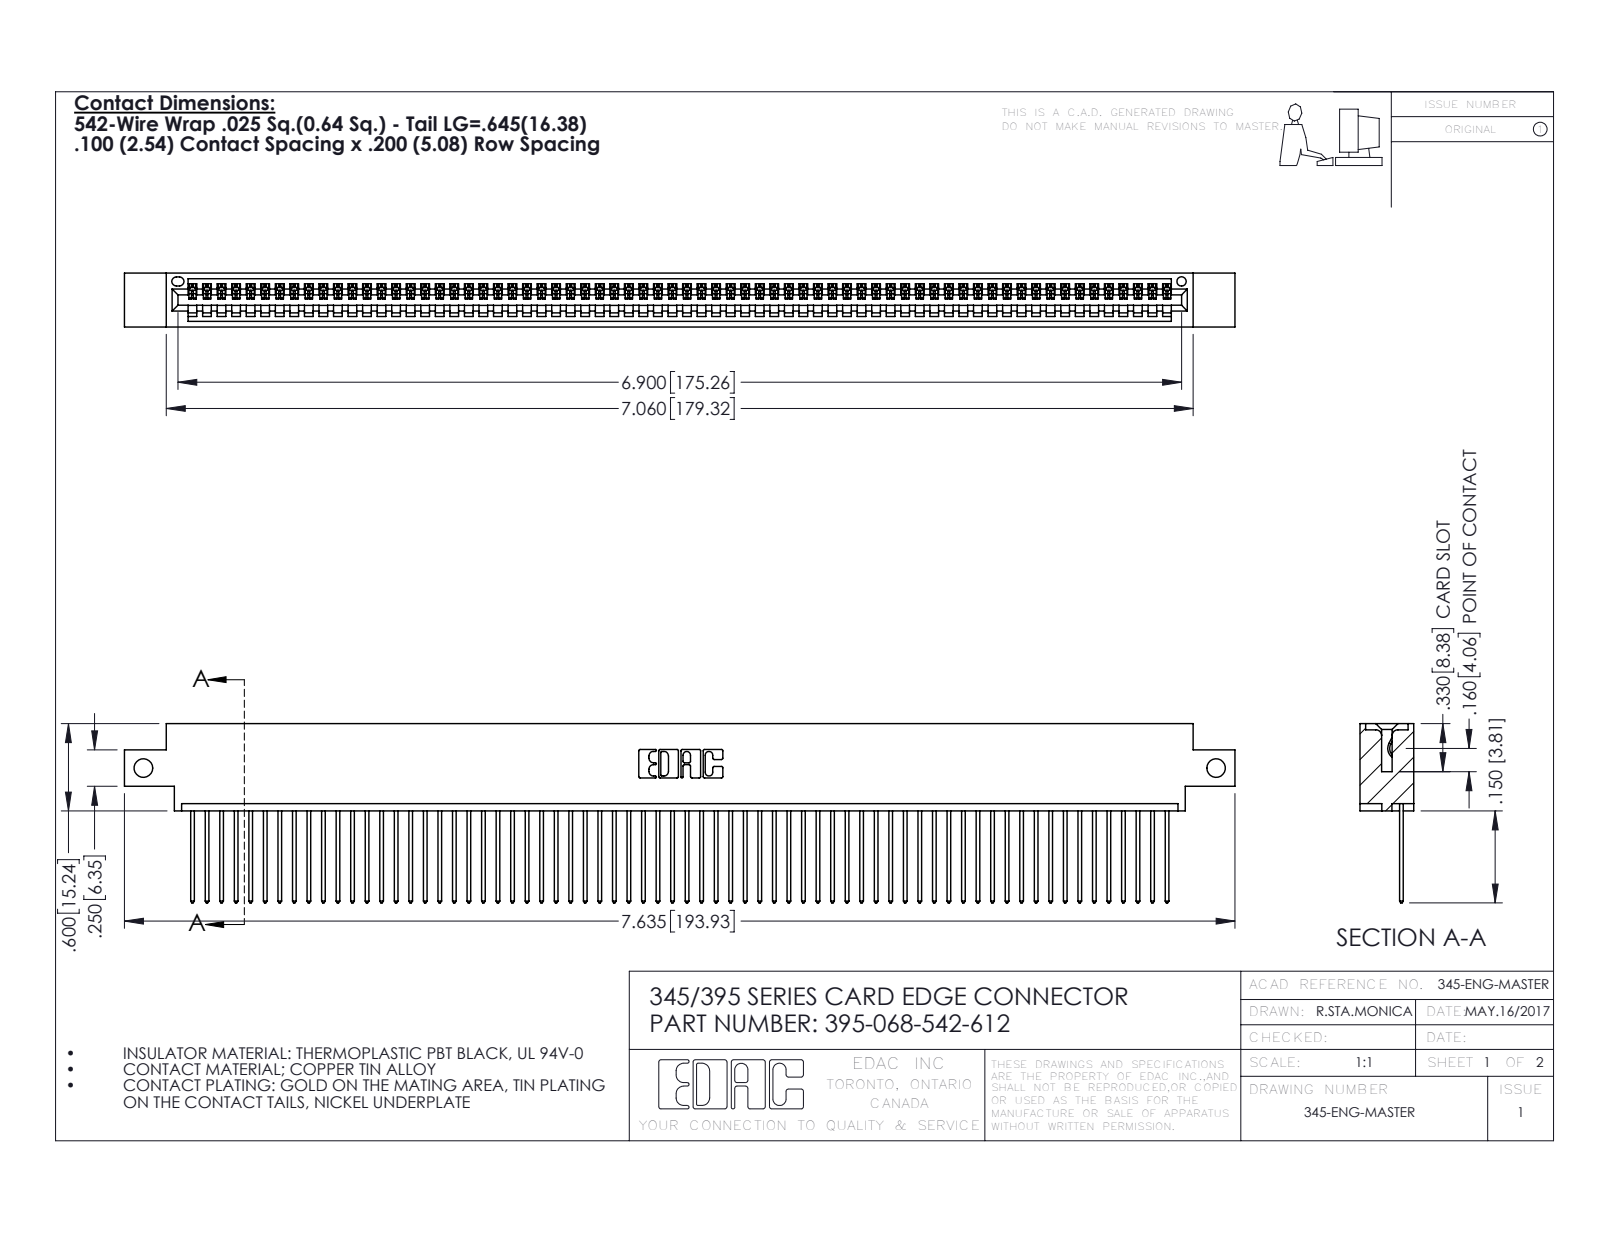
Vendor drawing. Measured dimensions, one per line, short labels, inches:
name: 395-068-542-612; 345-292-001_345-293-142; 345 Part_0.170 Offset - Side Mount
written by: SolidWorks 2016 (CONFIG_CONTROL_DESIGN)
unit: in
bodies: 69 solids, 4074 faces (2804 planar, 1270 cylindrical, 0 other)
size: 7.635 × 1.232 × 0.37
volume: 1.134 in³; area: 40.28 in²
holes: 2× ⌀0.128, 1× ⌀0.064
rounds: 136× R0.006, 136× R0.01, 22× R0.01, 6× R0.007, 6× R0.031, 3× R0.026, 2× R0.031, 2× R0.04
face distances: 0.072, 0.298, 0.37, 0.098, 0.272, 0.025, 0.2, 0.225, 0.175, 0.149
hole spacings: 7.375
